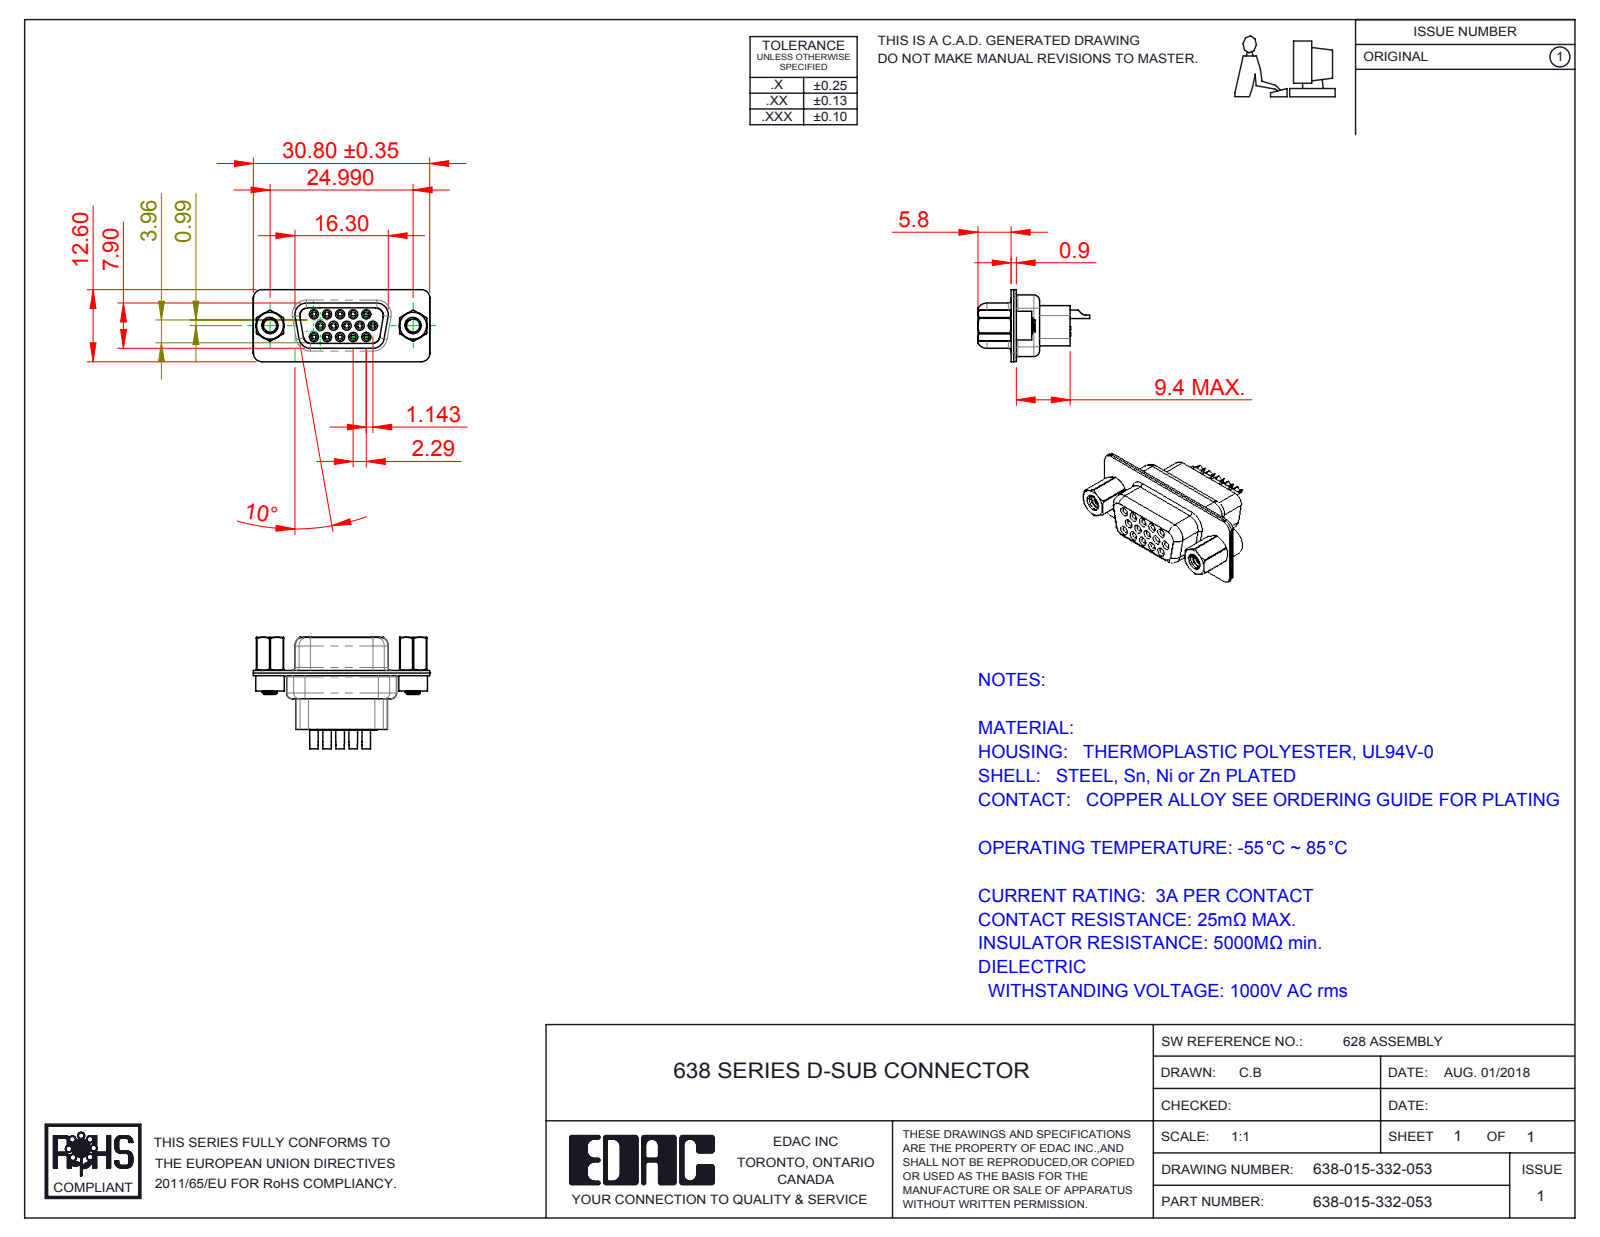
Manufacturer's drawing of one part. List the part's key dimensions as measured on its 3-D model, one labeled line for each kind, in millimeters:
Part name (STEP PRODUCT): 638 Contact Row 2_32H; 638 Housing_15 Contacts HP; 638-015-332-053; 638 Shell Front_15 Contacts (+5 more)
STEP written by: SolidWorks 2016 (CONFIG_CONTROL_DESIGN)
Units: millimetres
Bodies: 22 solids, 1740 faces (404 planar, 584 cylindrical, 752 other)
Overall size (bounding box): 30.81 × 19.5 × 12.6
Volume: 2 078 mm³ · Surface area: 6 797 mm²
Round holes (diameter × count): ⌀0.8 ×15, ⌀1 ×15, ⌀1.1 ×15, ⌀1.6 ×15, ⌀1.7 ×15, ⌀1.8 ×15, ⌀2 ×2, ⌀2.26 ×2, ⌀2.29 ×2, ⌀4 ×2, ⌀4.05 ×2, ⌀4.85 ×2
Round bosses / shafts (diameter × count): ⌀2 ×15, ⌀1.5 ×15, ⌀1.2 ×15, ⌀5 ×2, ⌀4.95 ×2, ⌀4.8 ×2, ⌀2.79 ×2
Partial cylindrical surfaces — rounded edges, fillets, slot ends (radius × count): R1.5 ×20, R2 ×12, R0.28 ×10, R1.55 ×8, R1 ×7, R1.35 ×5, R0.25 ×4, R0.5 ×4
Main face-to-face distances: 0.45, 0.9, 0.4, 1.43, 8.88, 6.6, 7, 9.4, 5.8, 2.28
Hole centre spacings: 3.96, 2.28, 4.57, 2.29, 6.05, 6.04, 6.86, 7.92
